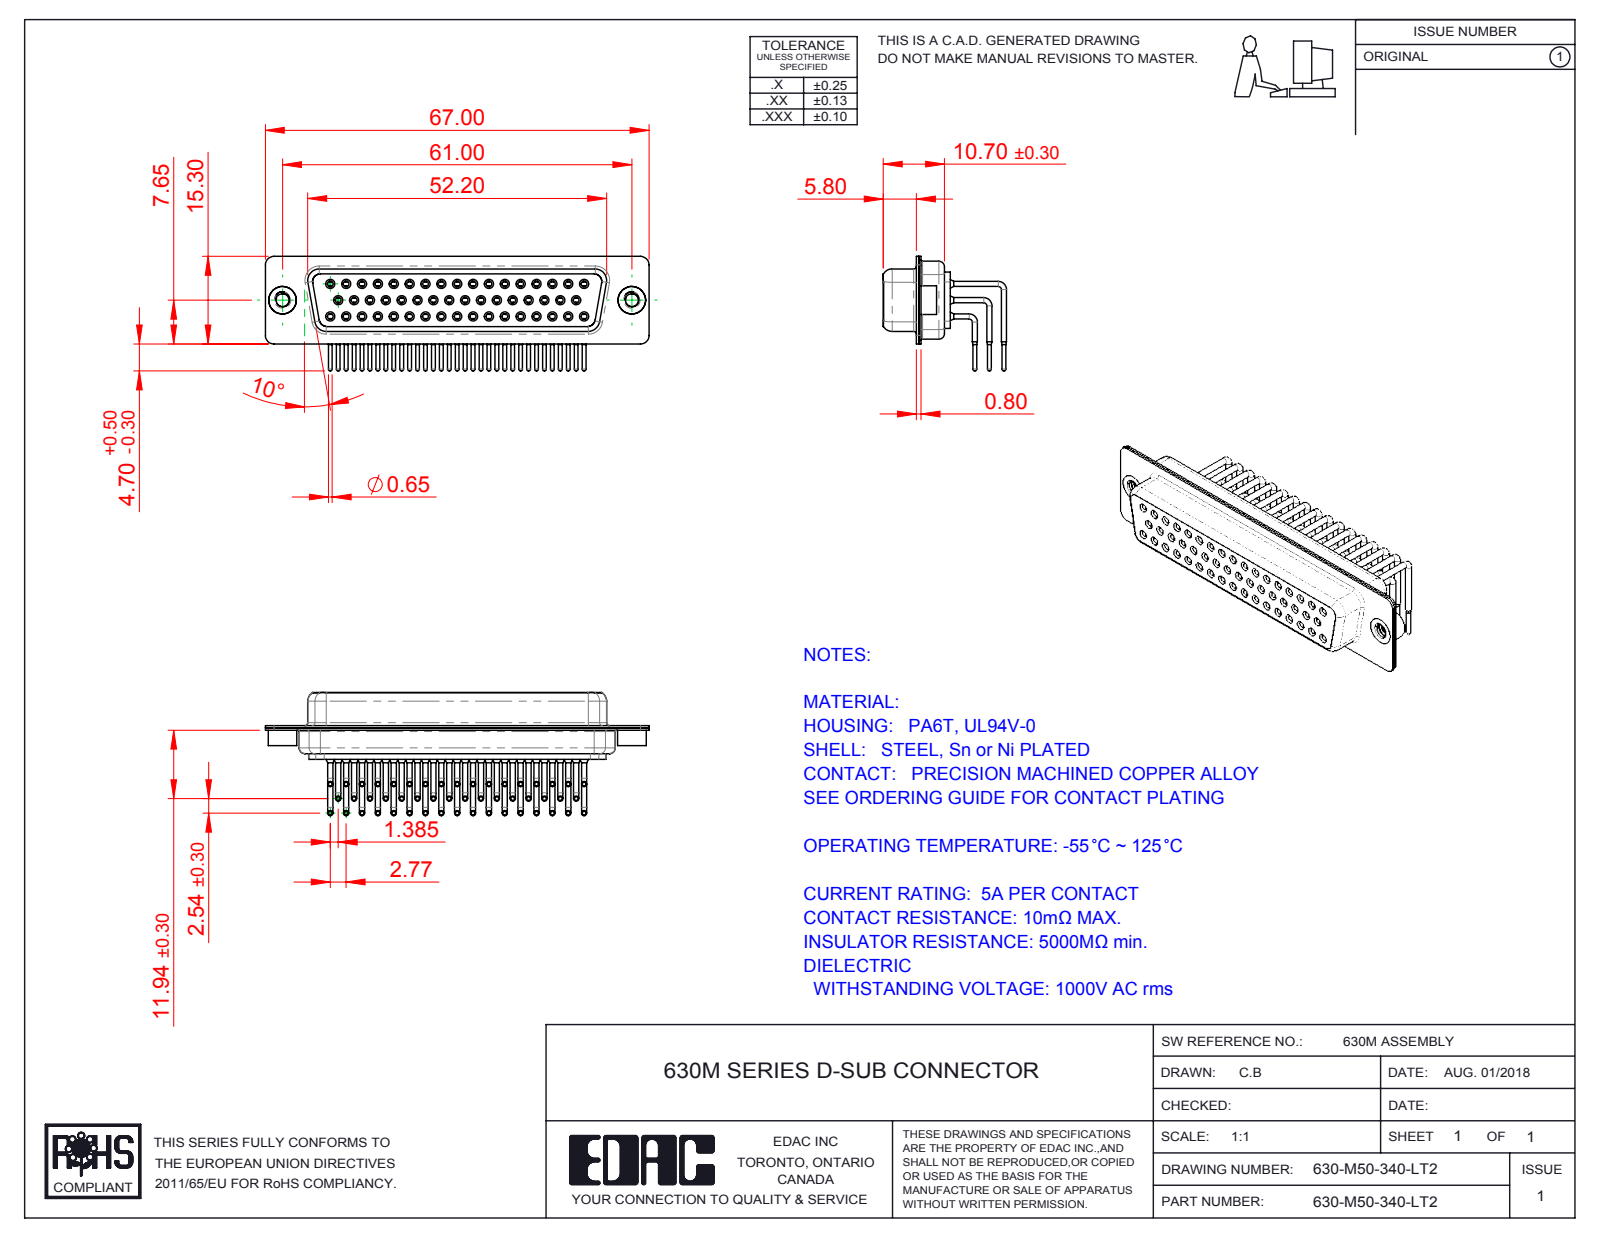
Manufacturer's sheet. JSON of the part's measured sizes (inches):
{"part_name": "630M Contact Row 1_50 Contacts; 630M Contact Row 2_50 Contacts; 630M Housing_50 Contacts; 630M Contact Row 3 (+4 more)", "step_written_by": "SolidWorks 2016 (CONFIG_CONTROL_DESIGN)", "units": "inches", "bodies": {"solids": 55, "faces": 2929, "planar": 817, "cylindrical": 1287, "other": 825}, "overall_size": [2.638, 0.848, 0.787], "volume_in3": 0.428, "surface_area_in2": 25.67, "round_holes": [[0.039, 50], [0.043, 50], [0.067, 50], [0.071, 50], [0.079, 50], [0.089, 2], [0.157, 2], [0.189, 2]], "round_bosses_or_shafts": [[0.035, 100], [0.063, 50], [0.059, 50], [0.026, 50], [0.197, 2], [0.193, 2]], "partial_cylinders_radius": [[0.059, 16], [0.079, 12], [0.053, 8], [0.063, 8], [0.01, 4], [0.02, 4], [0.024, 4], [0.026, 4]], "face_to_face_distances": [0.016, 0.053, 0.467, 0.033, 0.087, 0.217, 0.482, 0.232, 0.413, 0.031], "hole_center_spacings": [0.109, 0.124, 0.218, 0.327, 0.436, 0.545, 0.654, 0.763]}
